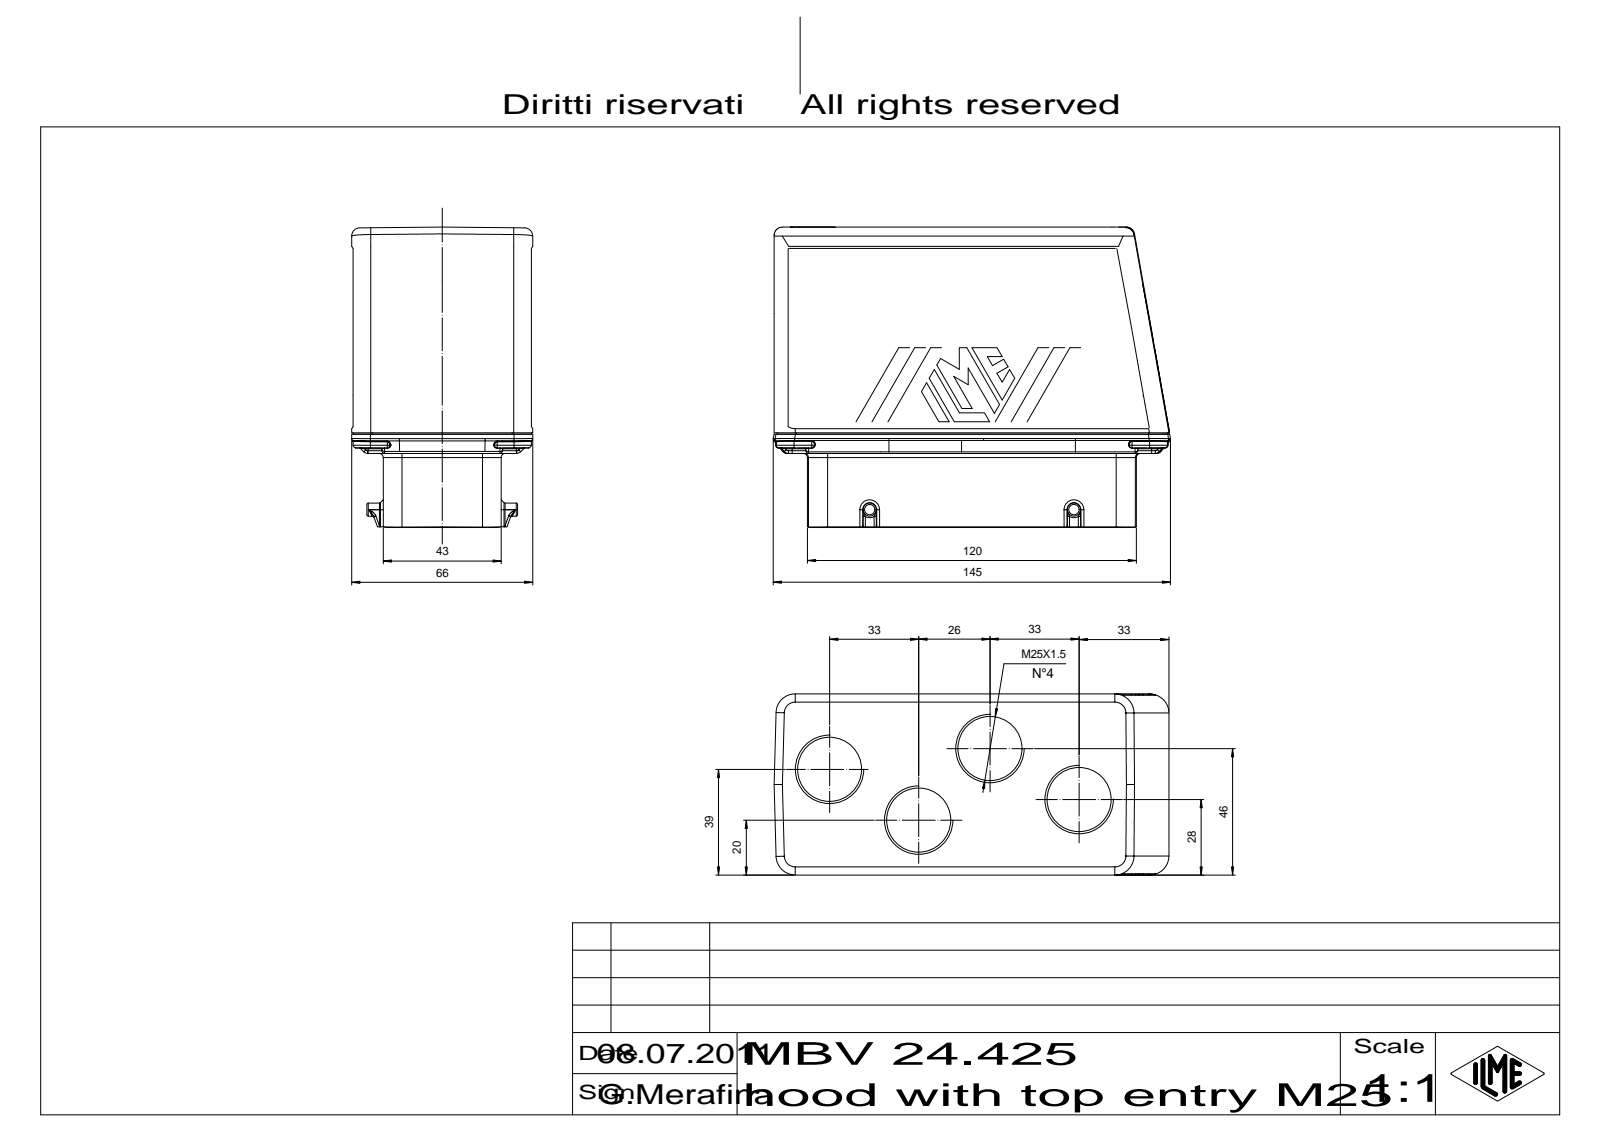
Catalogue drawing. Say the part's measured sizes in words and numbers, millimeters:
The part is named "53848". Its 3-D file was written by "CoCreate Modeling 16.00A 16-Aug-2008 (C) Parametric Technology GmbH (AUTOMOTIVE_DESIGN)". It is 1 solid with 699 faces: 379 planar, 130 cylindrical and 190 other. Overall it measures 143.75 by 108.97 by 66.01 millimeters. Its volume is 705 547 cubic millimeters and its surface area 76 416 square millimeters. Round holes: 4 of diameter 23.4. Round bosses or shafts: 2 of diameter 4.8. Partial cylindrical surfaces (rounded edges, fillets, slot ends): 44 of radius 1, 12 of radius 7, 8 of radius 0.5, 6 of radius 0.3, 6 of radius 1.5, 6 of radius 3, 4 of radius 4.2, 4 of radius 5. The main face-to-face distances are 65.01, 82.21, 0.4, 65.41, 11, 54.01, 54, 43, 11.01, 54.41. The hole center spacings are 36.82, 37.4, 37.43, 58.98, 58.99, 91.66.
